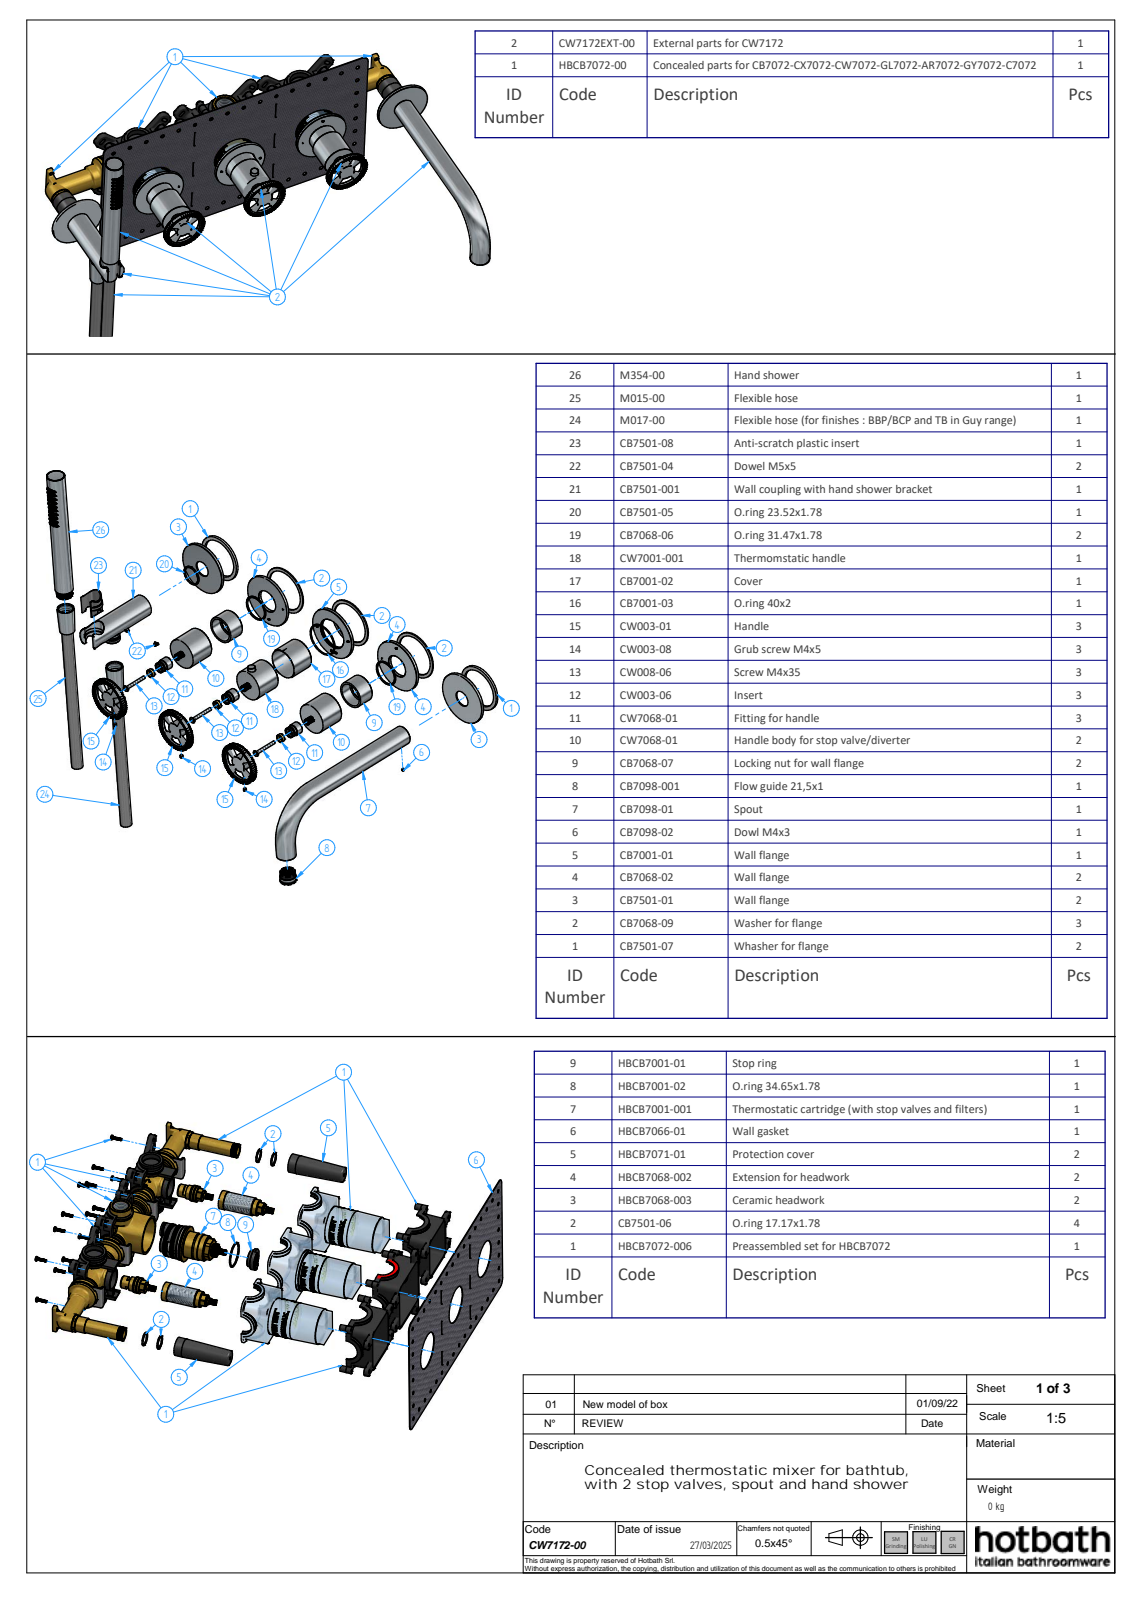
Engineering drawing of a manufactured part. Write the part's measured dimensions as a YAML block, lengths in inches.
part_name: "CW7172EXT-00; CB7098-01; CB7098-02; CB7098-001 (+8 more)"
step_written_by: "Solid Edge (AUTOMOTIVE_DESIGN)"
units: inches
bodies: {solids: 34, faces: 6574, planar: 1054, cylindrical: 1944, other: 3576}
overall_size: [21.732, 18.252, 10.165]
volume: 22.02
surface_area: 395.5
round_holes:
  - {diameter: 0.126, count: 41}
  - {diameter: 0.128, count: 4}
  - {diameter: 0.591, count: 4}
  - {diameter: 0.177, count: 3}
  - {diameter: 0.197, count: 3}
  - {diameter: 0.287, count: 3}
  - {diameter: 0.445, count: 3}
  - {diameter: 0.453, count: 3}
  - {diameter: 0.472, count: 3}
  - {diameter: 0.866, count: 3}
  - {diameter: 1.516, count: 3}
  - {diameter: 2.638, count: 3}
round_bosses_or_shafts:
  - {diameter: 2.835, count: 5}
  - {diameter: 0.63, count: 5}
  - {diameter: 2.244, count: 3}
  - {diameter: 1.654, count: 3}
  - {diameter: 0.866, count: 3}
  - {diameter: 0.551, count: 3}
  - {diameter: 0.492, count: 3}
  - {diameter: 0.157, count: 3}
partial_cylinders:
  - {radius: 0.008, count: 346}
  - {radius: 0.024, count: 336}
  - {radius: 0.311, count: 336}
  - {radius: 0.039, count: 50}
  - {radius: 0.004, count: 48}
  - {radius: 0.02, count: 8}
  - {radius: 0.012, count: 6}
  - {radius: 0.014, count: 4}
face_to_face_distances: [0.157, 0.059, 0.039, 0.118, 2.024, 0.098, 0.111, 0.023, 0.017, 0.076]
hole_center_spacings: [0.284, 0.498, 0.236, 0.472, 0.726, 0.157, 0.709, 0.958]
